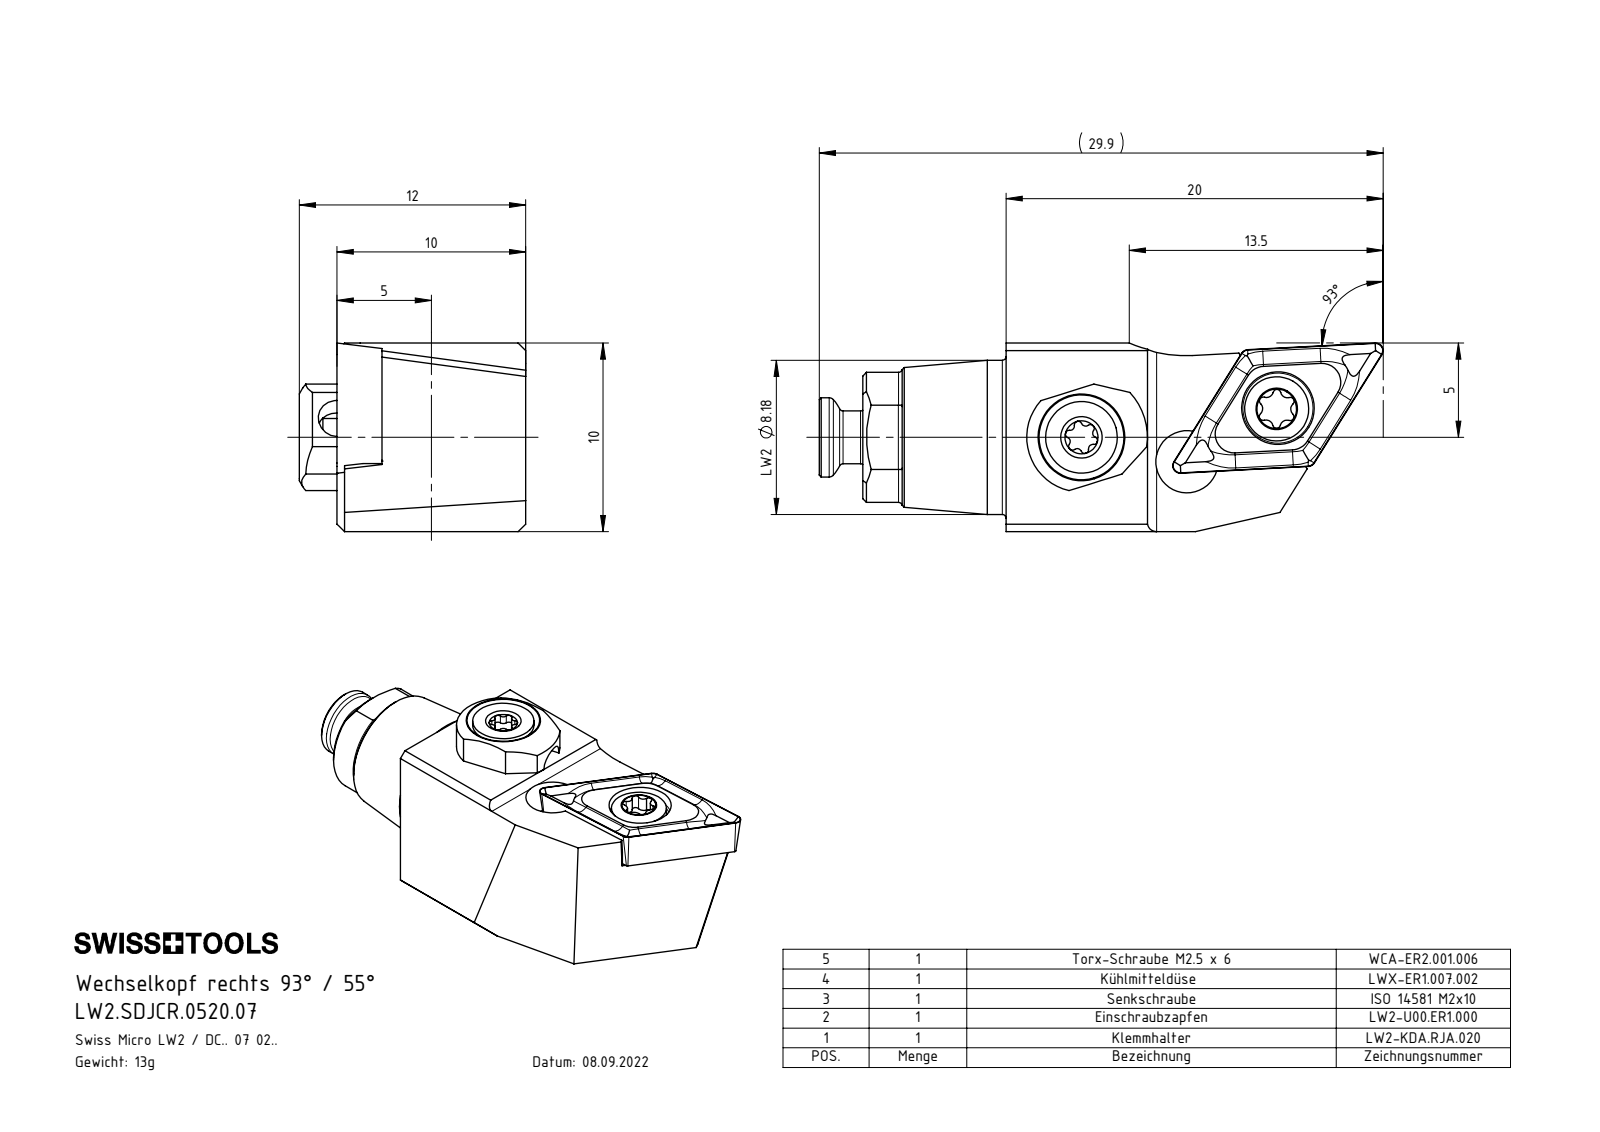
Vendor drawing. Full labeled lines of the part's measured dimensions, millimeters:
Part name (STEP PRODUCT): DCMT070204; LW2-KDA.RJA.020_A; ISO 14581 - M2x10; LWX-ER1.007.002 (+3 more)
STEP written by: SolidWorks 2022 (CONFIG_CONTROL_DESIGN)
Units: millimetres
Bodies: 6 solids, 260 faces (66 planar, 94 cylindrical, 100 other)
Overall size (bounding box): 29.9 × 12 × 10
Volume: 1 785 mm³ · Surface area: 1 723 mm²
Round holes (diameter × count): ⌀1 ×1, ⌀1.5 ×1, ⌀1.6 ×1, ⌀2.05 ×1, ⌀2.8 ×1, ⌀3 ×1, ⌀3.3 ×1, ⌀3.5 ×1, ⌀3.85 ×1
Round bosses / shafts (diameter × count): ⌀8.18 ×1, ⌀4.2 ×1, ⌀4 ×1, ⌀3.8 ×1, ⌀3.4 ×1, ⌀3 ×1, ⌀2.8 ×1, ⌀2.5 ×1
Partial cylindrical surfaces — rounded edges, fillets, slot ends (radius × count): R0.2 ×8, R0.19 ×6, R0.21 ×6, R0.24 ×6, R0.29 ×6, R0.36 ×5, R0.36 ×1, R0.5 ×1
Main face-to-face distances: 10, 7.62, 2.38, 9.6, 1.98, 0.4, 7.6, 2, 1.1, 8
Hole centre spacings: 5.52, 5.59, 5.75, 10.47, 10.53
